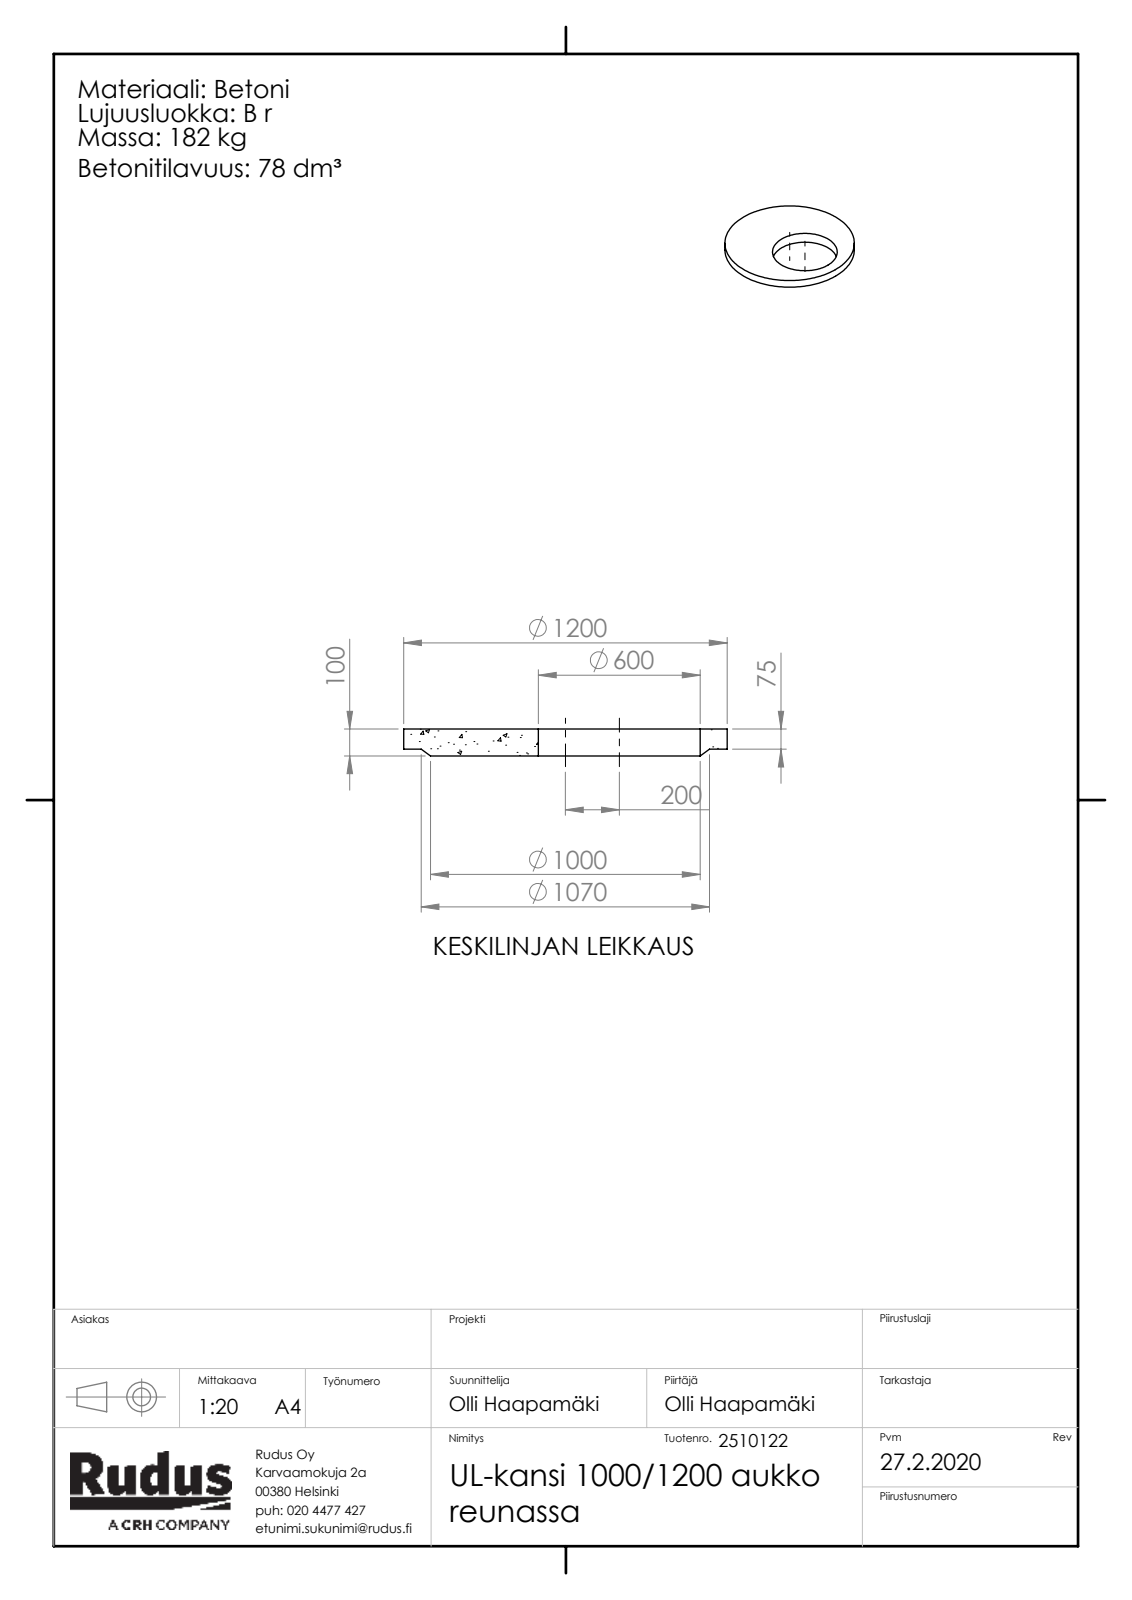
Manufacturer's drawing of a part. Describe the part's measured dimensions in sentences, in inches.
The part is named "UL-osa-kansi_aukko; Rudus 2510122 UL-kansi 1000_1200 aukko reunassa". Its 3-D file was written by "SolidWorks 2019 (CONFIG_CONTROL_DESIGN)". It is 1 solid with 9 faces: 3 planar, 4 cylindrical and 2 other. Overall it measures 47.244 by 47.244 by 3.937 inches. Its volume is 4 735 cubic inches and its surface area 3 401 square inches. Round holes: 1 of diameter 23.622. Round bosses or shafts: 1 of diameter 47.244. The main face-to-face distances are 3.937, 0.984, 2.953.
